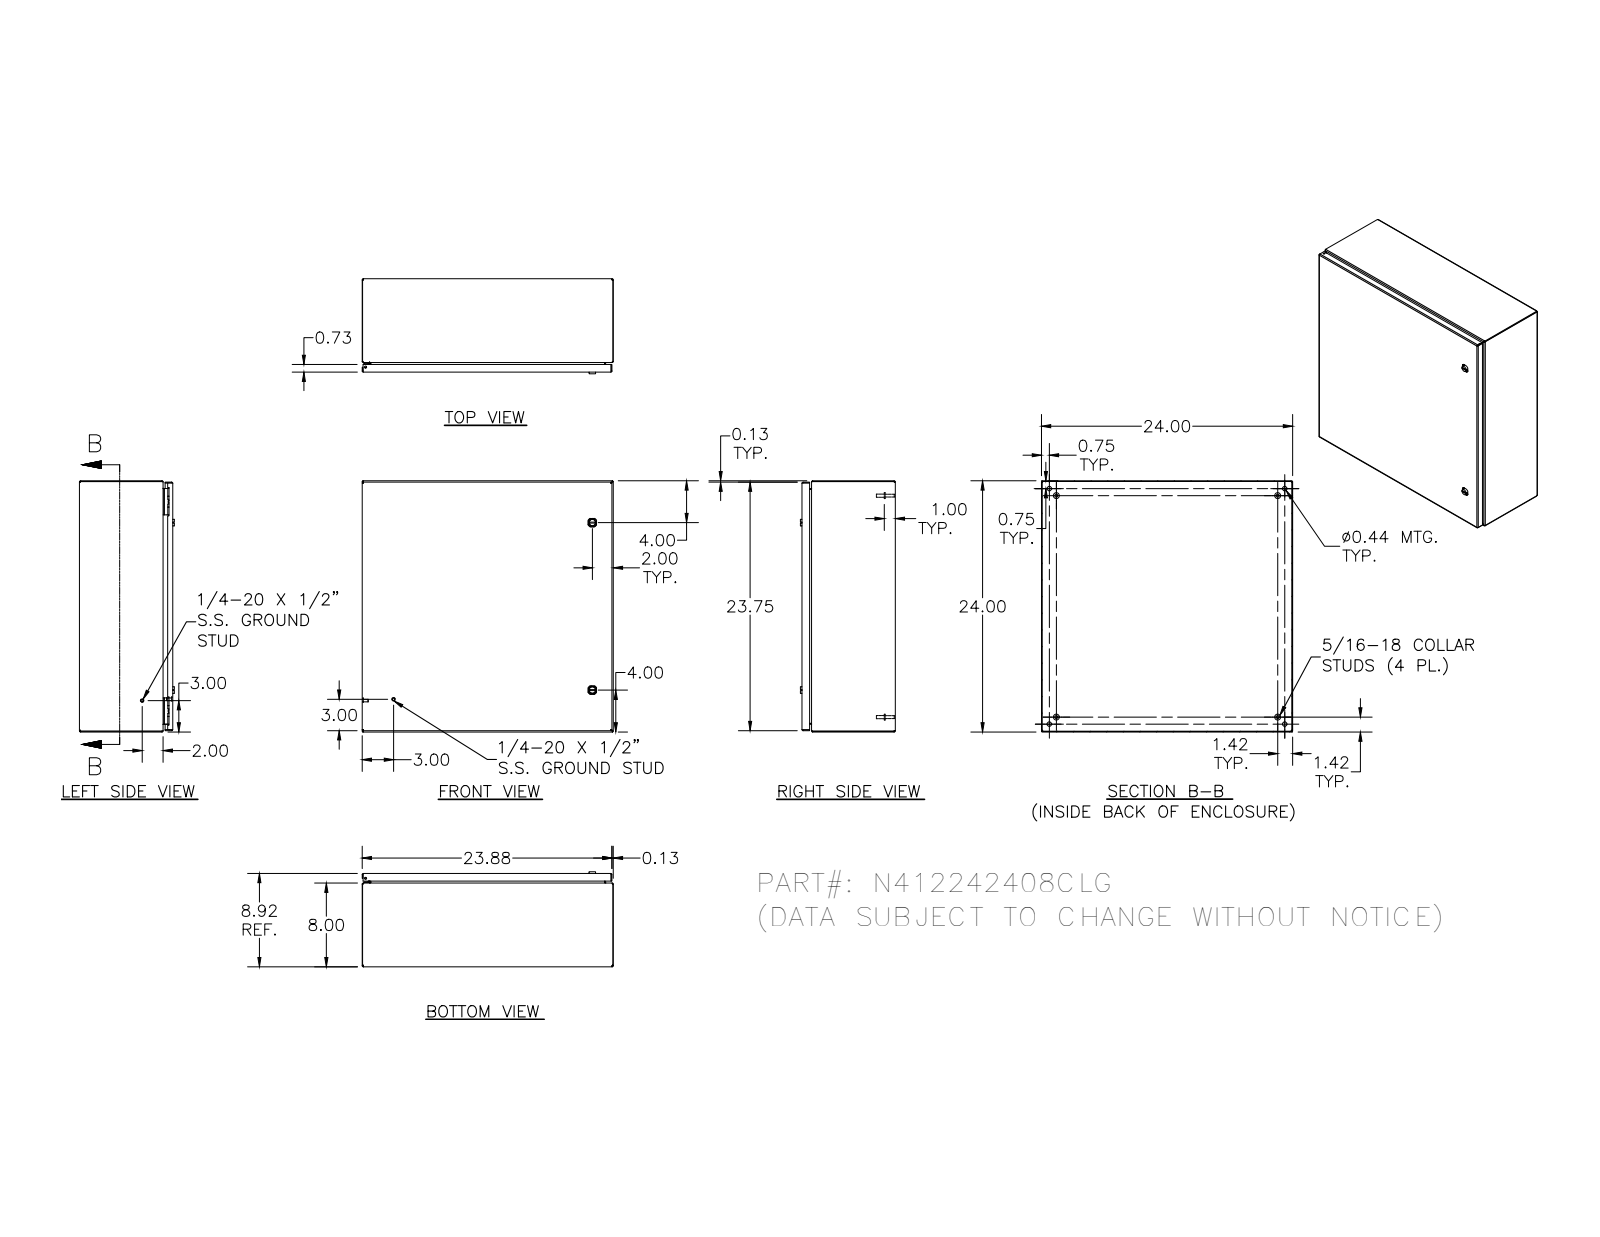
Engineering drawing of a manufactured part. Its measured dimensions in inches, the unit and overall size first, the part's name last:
Units: inches
Overall size (bounding box): 24 × 24 × 9.075
Round holes (diameter × count): ⌀0.188 ×5, ⌀0.093 ×4, ⌀0.152 ×4, ⌀0.167 ×4, ⌀0.172 ×4, ⌀0.437 ×4, ⌀0.156 ×2, ⌀0.197 ×2, ⌀0.315 ×2, ⌀0.394 ×2, ⌀0.402 ×2, ⌀0.634 ×2
Round bosses / shafts (diameter × count): ⌀0.25 ×10, ⌀0.563 ×4, ⌀0.36 ×4, ⌀0.32 ×4, ⌀0.3 ×4, ⌀0.256 ×4, ⌀0.164 ×4, ⌀0.131 ×4
Partial cylindrical surfaces — rounded edges, fillets, slot ends (radius × count): R0.012 ×54, R0.031 ×30, R0.05 ×26, R0.02 ×23, R0.105 ×20, R0.016 ×18, R0.125 ×16, R0.032 ×8
Main face-to-face distances: 0.074, 8.843, 8.769, 8.917, 0.074, 23.926, 23.926, 24, 23.852, 0.917
Hole centre spacings: 20, 0.66, 0.656, 1.307, 1.965, 19.34, 20.66, 1.619
Volume: 157 in³ · Surface area: 4 258 in²
Bodies: 40 solids, 1812 faces (704 planar, 676 cylindrical, 432 other)
Part name (STEP PRODUCT): N412242408CLG
STEP written by: SolidWorks 2018 (AUTOMOTIVE_DESIGN)
